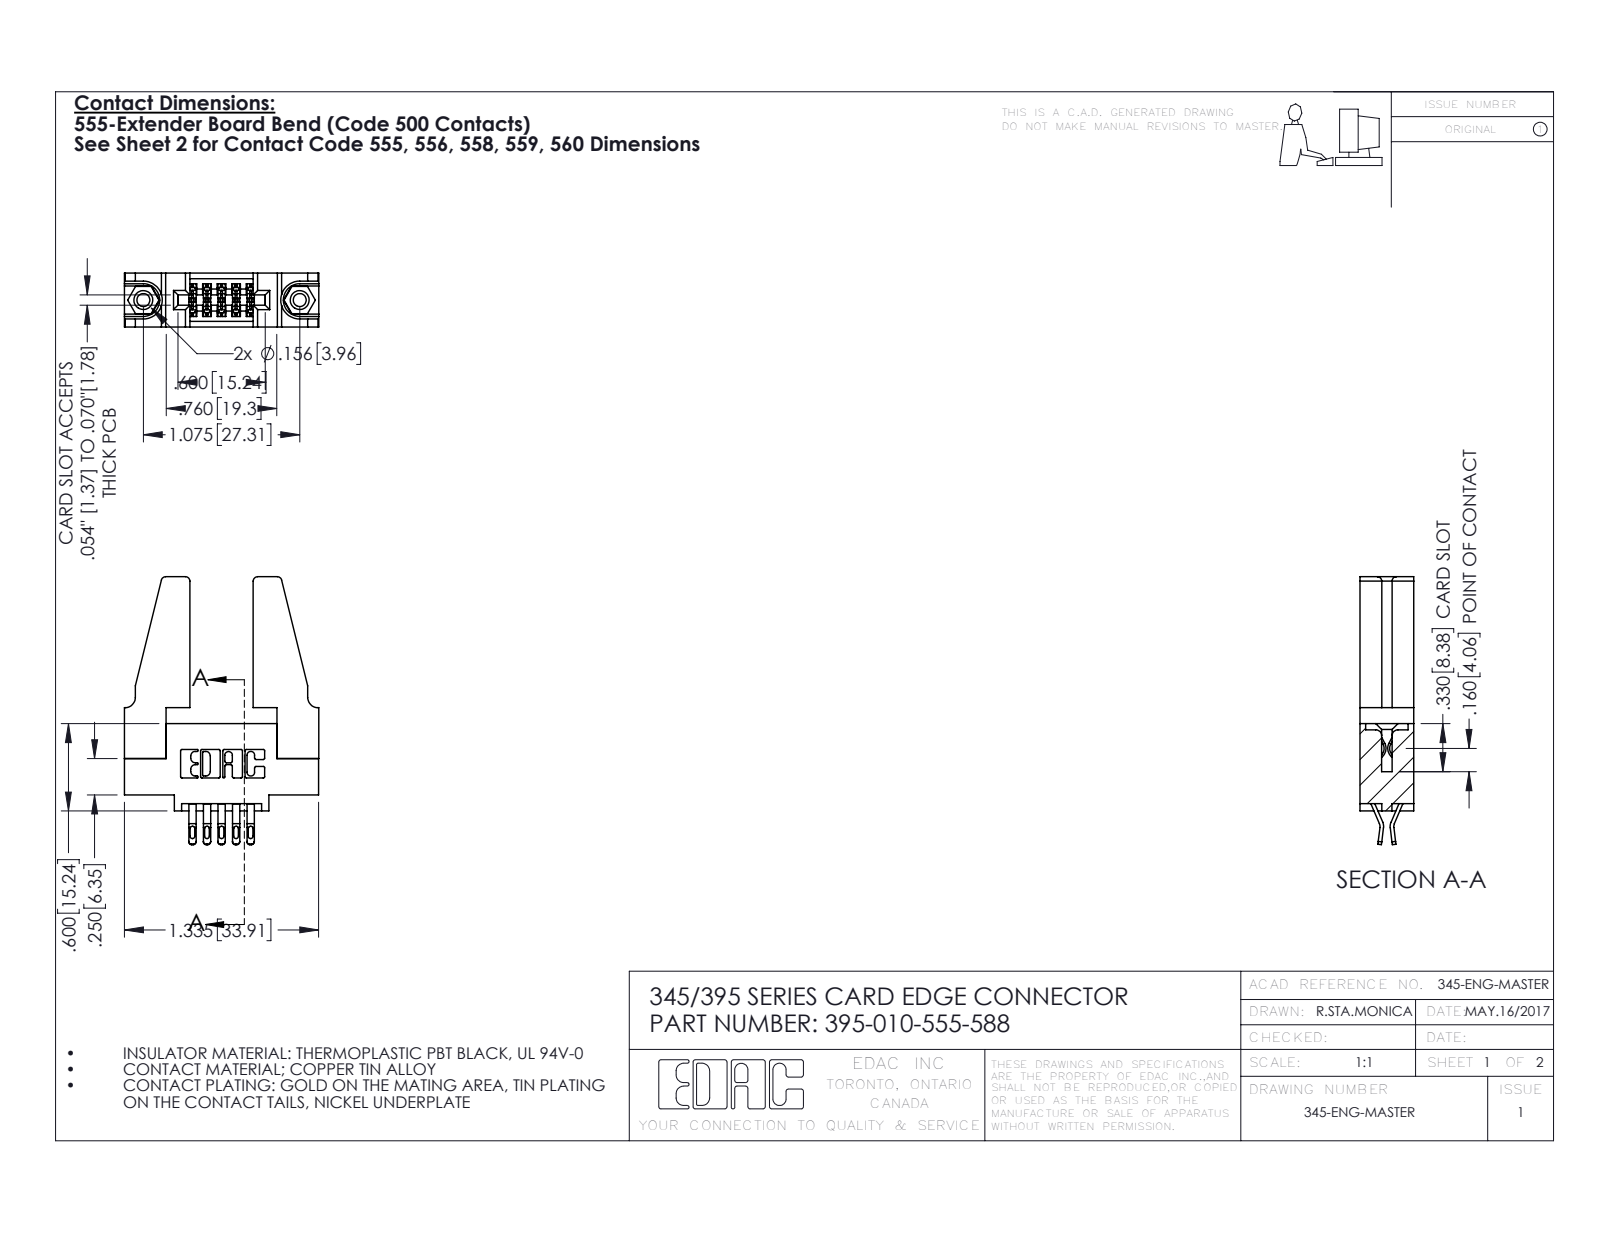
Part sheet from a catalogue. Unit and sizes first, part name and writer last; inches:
Units: inches
Overall size (bounding box): 1.842 × 1.336 × 0.37
Round holes (diameter × count): ⌀0.089 ×2, ⌀0.125 ×2, ⌀0.156 ×2, ⌀0.064 ×1
Round bosses / shafts (diameter × count): ⌀0.155 ×2
Partial cylindrical surfaces — rounded edges, fillets, slot ends (radius × count): R0.016 ×25, R0.01 ×22, R0.02 ×20, R0.006 ×15, R0.03 ×8, R0.007 ×6, R0.031 ×6, R0.026 ×3
Main face-to-face distances: 0.37, 0.072, 0.298, 0.2, 0.148, 0.15, 0.025, 0.22, 0.077, 0.45
Hole centre spacings: 0.27, 0.847, 1.075
Volume: 0.376 in³ · Surface area: 10.69 in²
Bodies: 15 solids, 814 faces (466 planar, 332 cylindrical, 16 other)
Part name (STEP PRODUCT): 395-010-555-588; 345 Part_0.110 Offset - 0.156 Dia-TH; 345-292-001_555 Tail; 345-250-001_345-250-001-102 (+1 more)
STEP written by: SolidWorks 2016 (CONFIG_CONTROL_DESIGN)
